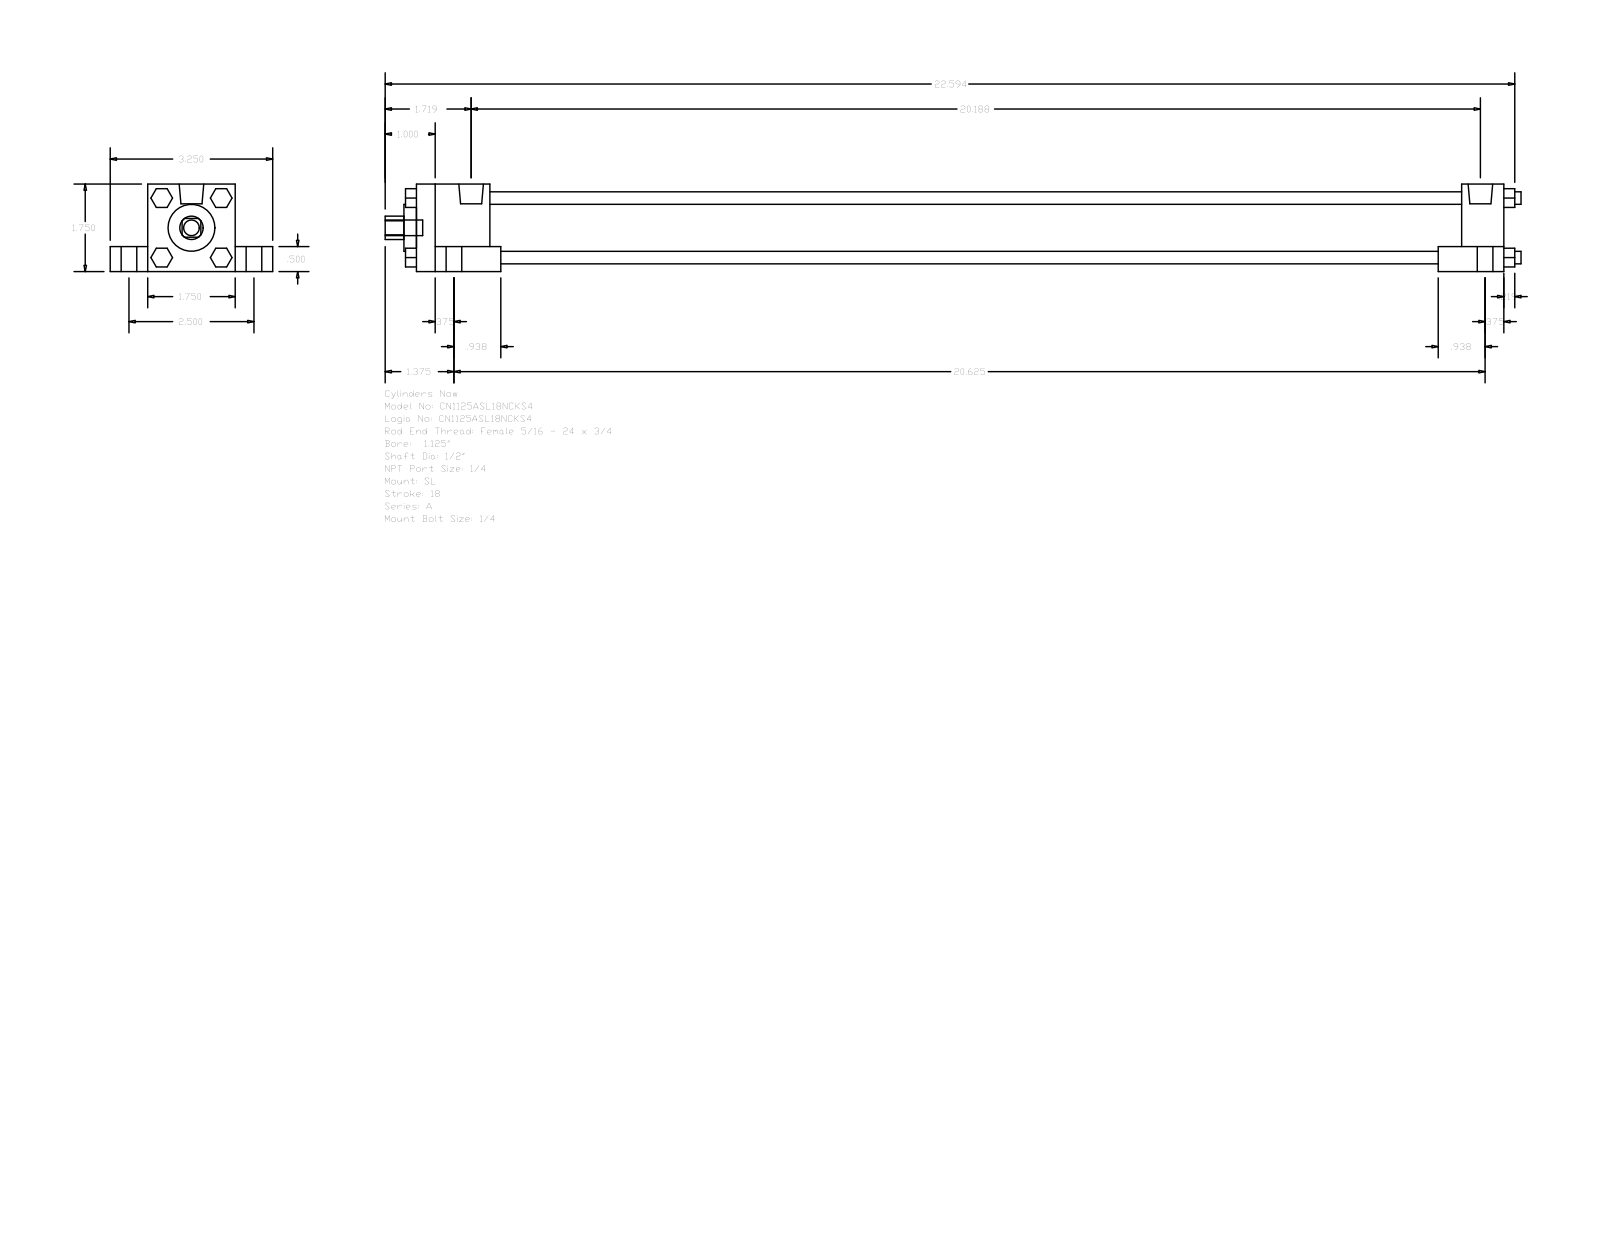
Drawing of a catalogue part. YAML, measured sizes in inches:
part_name: "A_SL__0112_0.5"
step_written_by: "GSSL Pune (CONFIG_CONTROL_DESIGN)"
units: inches
bodies: {solids: 0, faces: 150, planar: 114, cylindrical: 36, other: 0}
overall_size: [22.719, 3.25, 1.75]
round_holes:
  - {diameter: 0.5, count: 1}
  - {diameter: 0.937, count: 1}
  - {diameter: 1.255, count: 1}
round_bosses_or_shafts:
  - {diameter: 0.313, count: 5}
  - {diameter: 0.563, count: 4}
  - {diameter: 0.25, count: 4}
  - {diameter: 0.219, count: 4}
  - {diameter: 0.492, count: 2}
partial_cylinders:
  - {radius: 0.234, count: 1}
face_to_face_distances: [1.75, 1.25, 0.5, 0.75, 2.5, 21.75, 20.906, 0.844, 1.469, 19.437]
